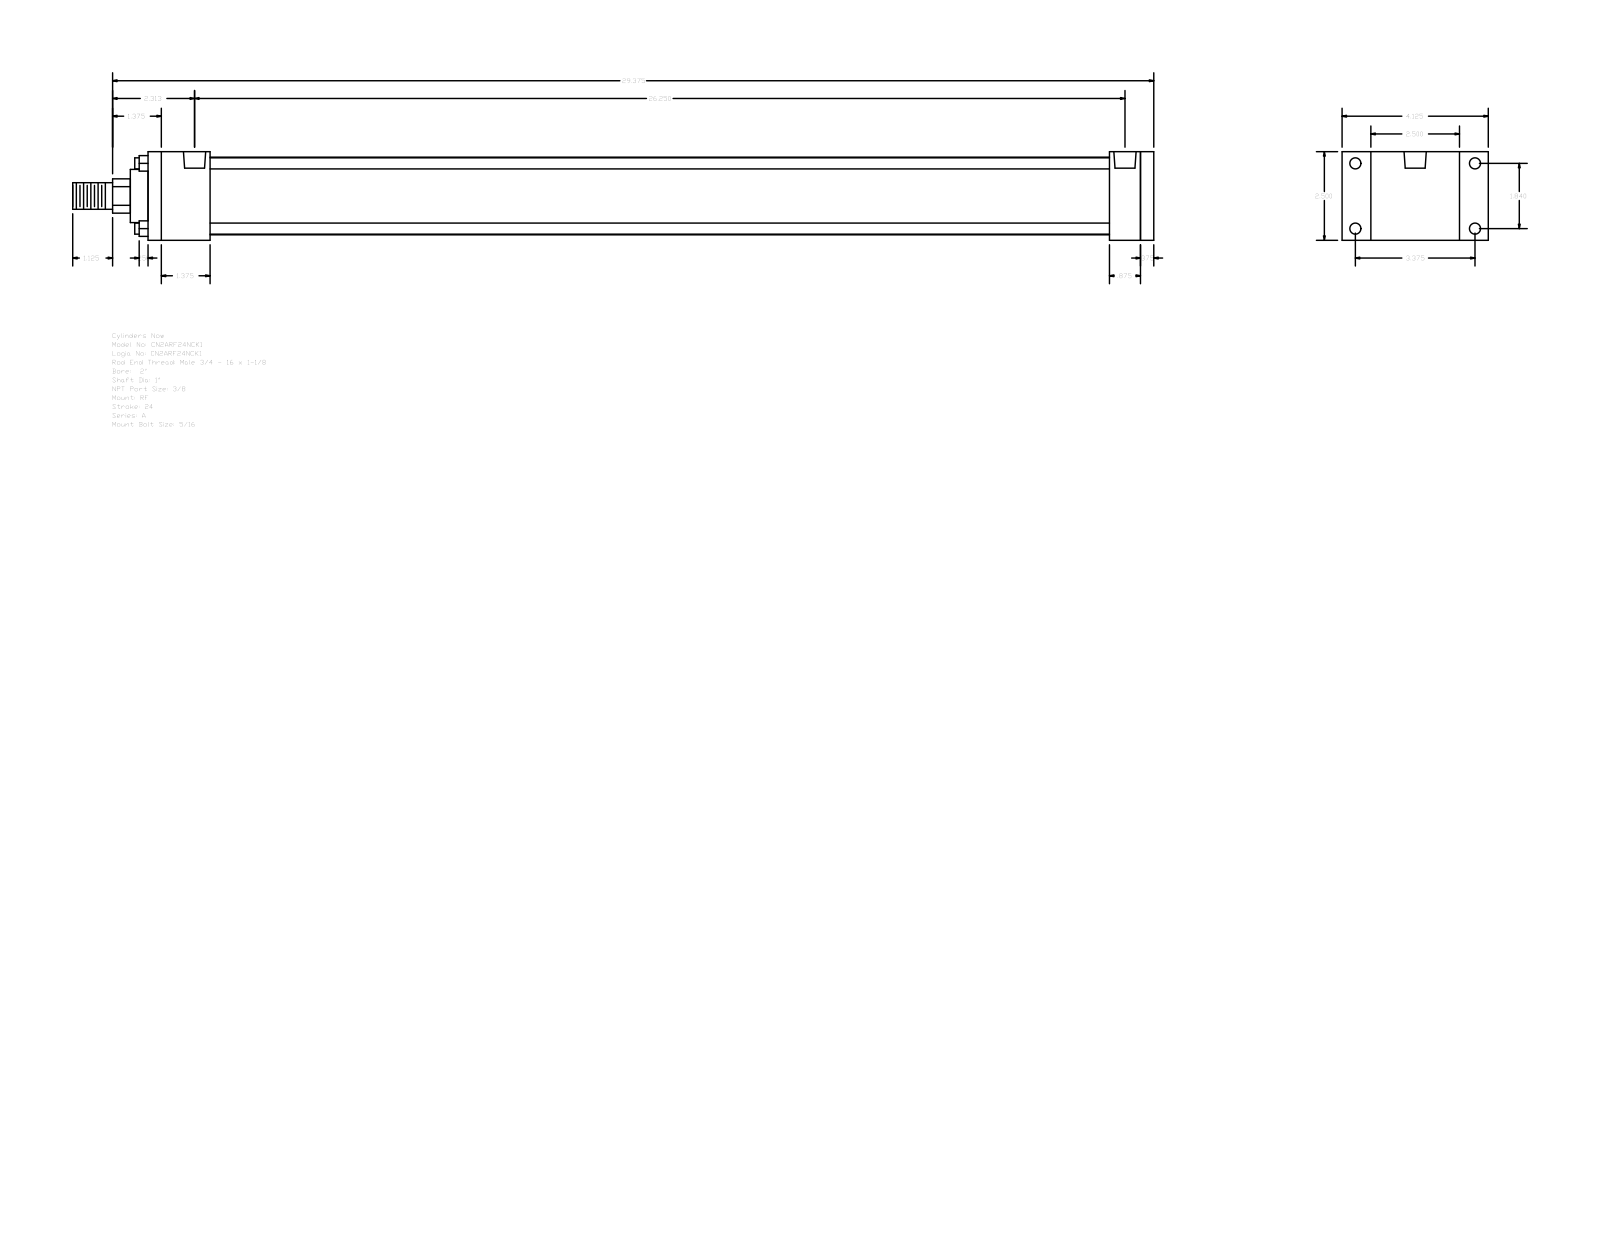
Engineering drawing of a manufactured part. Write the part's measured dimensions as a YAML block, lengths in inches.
part_name: "A_RF__0200_1"
step_written_by: "GSSL Pune (CONFIG_CONTROL_DESIGN)"
units: inches
bodies: {solids: 0, faces: 92, planar: 64, cylindrical: 28, other: 0}
overall_size: [30.5, 4.125, 2.5]
round_holes:
  - {diameter: 0.219, count: 4}
  - {diameter: 0.313, count: 4}
  - {diameter: 0.627, count: 2}
round_bosses_or_shafts:
  - {diameter: 0.313, count: 4}
  - {diameter: 2.19, count: 1}
  - {diameter: 1.5, count: 1}
  - {diameter: 1, count: 1}
  - {diameter: 0.75, count: 1}
partial_cylinders:
  - {radius: 0.484, count: 1}
face_to_face_distances: [2.5, 0.375, 28.375, 28, 1.75, 0.813, 26.25, 26.625, 27.125, 25.375]
hole_center_spacings: [1.84, 3.375, 3.844, 26.031, 0.063, 0.157, 26.093, 26.187]
